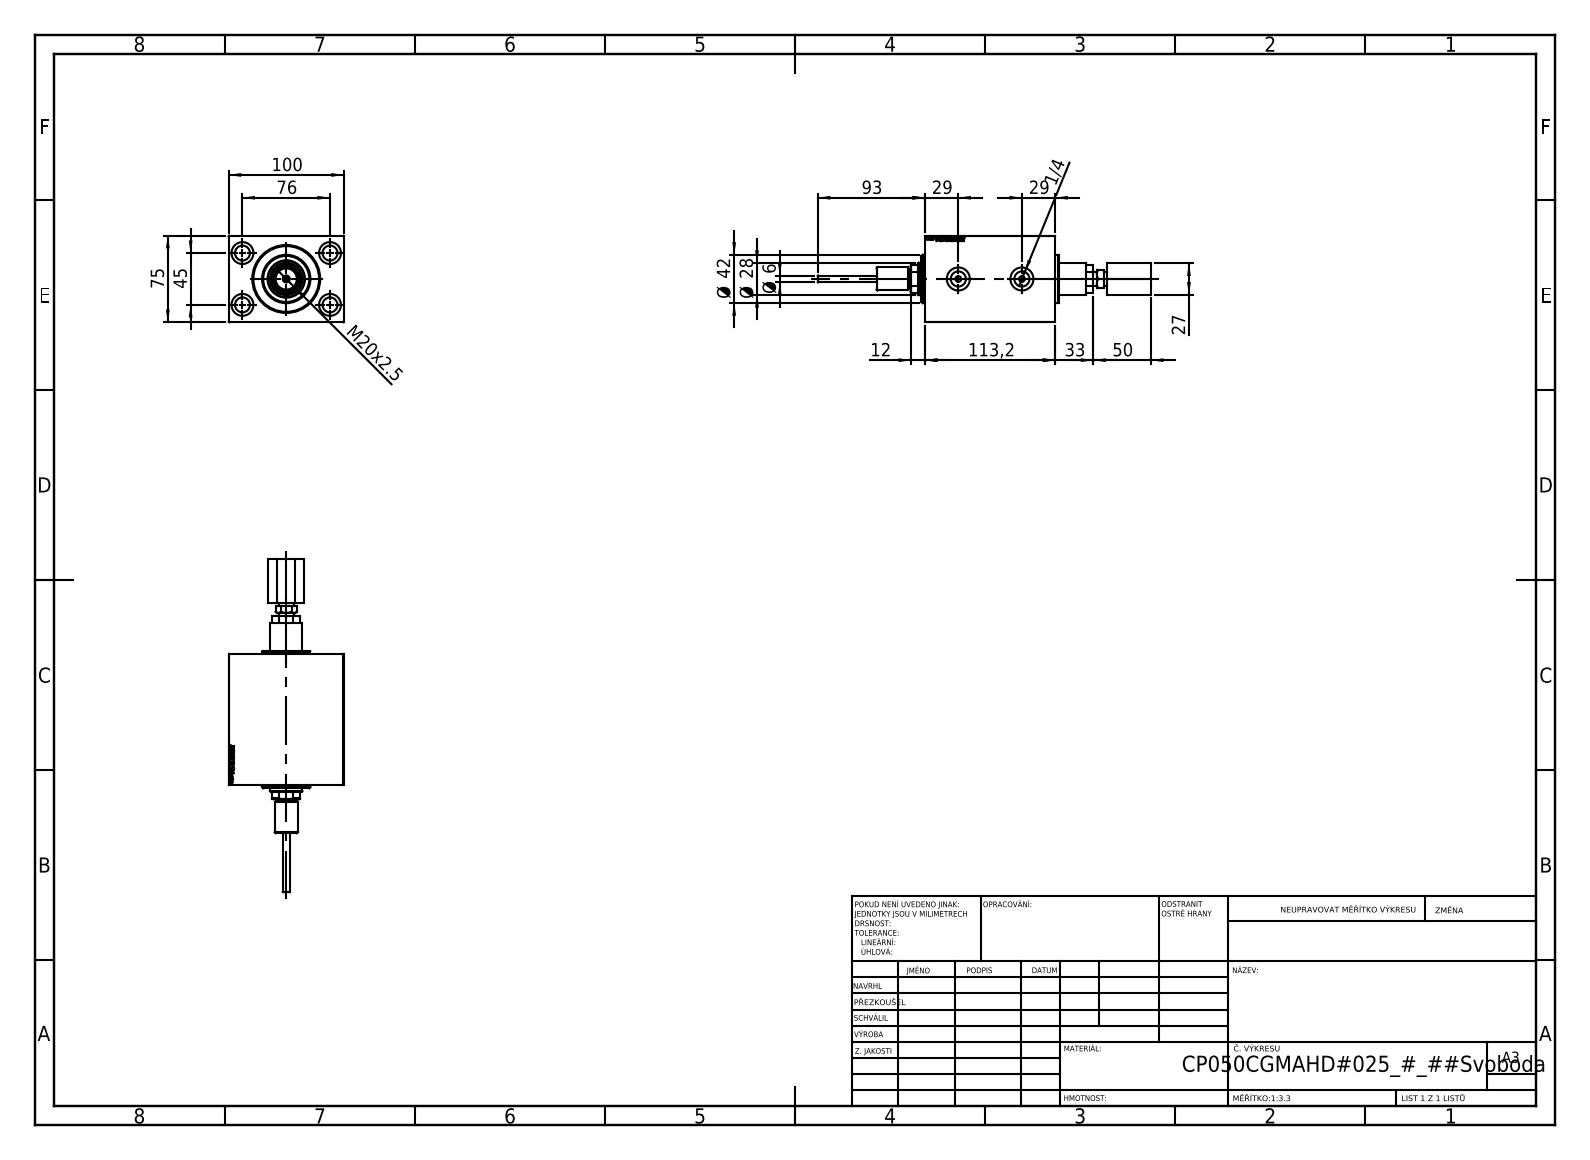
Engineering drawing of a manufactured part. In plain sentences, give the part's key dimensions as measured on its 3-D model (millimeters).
The part is named "V450DCP_VC_B; V450DCP_B_VCP; V450DCP_C_Body; V450DCP_B_RodCooling_ACCESSORIES (+1 more)". Its 3-D file was written by "SolidWorks 2019 (CONFIG_CONTROL_DESIGN)". It is 5 solids with 970 faces: 446 planar, 106 cylindrical and 418 other. Overall it measures 289.2 by 100 by 75 millimeters. Its volume is 792 604 cubic millimeters and its surface area 145 943 square millimeters. Round holes: 4 of diameter 13, 4 of diameter 19, 2 of diameter 4, 2 of diameter 5, 2 of diameter 9.73, 2 of diameter 13.16, 2 of diameter 15, 2 of diameter 20, 1 of diameter 3, 1 of diameter 6, 1 of diameter 18.5, 1 of diameter 28. Round bosses or shafts: 1 of diameter 42, 1 of diameter 20, 1 of diameter 18, 1 of diameter 12.78. Partial cylindrical surfaces (rounded edges, fillets, slot ends): 1 of radius 13.5. The main face-to-face distances are 75, 100, 99.2, 113.2, 14, 13, 1, 112.2, 55, 30. The hole center spacings are 44.16, 45, 76, 88.32, 42.55, 55.2.
